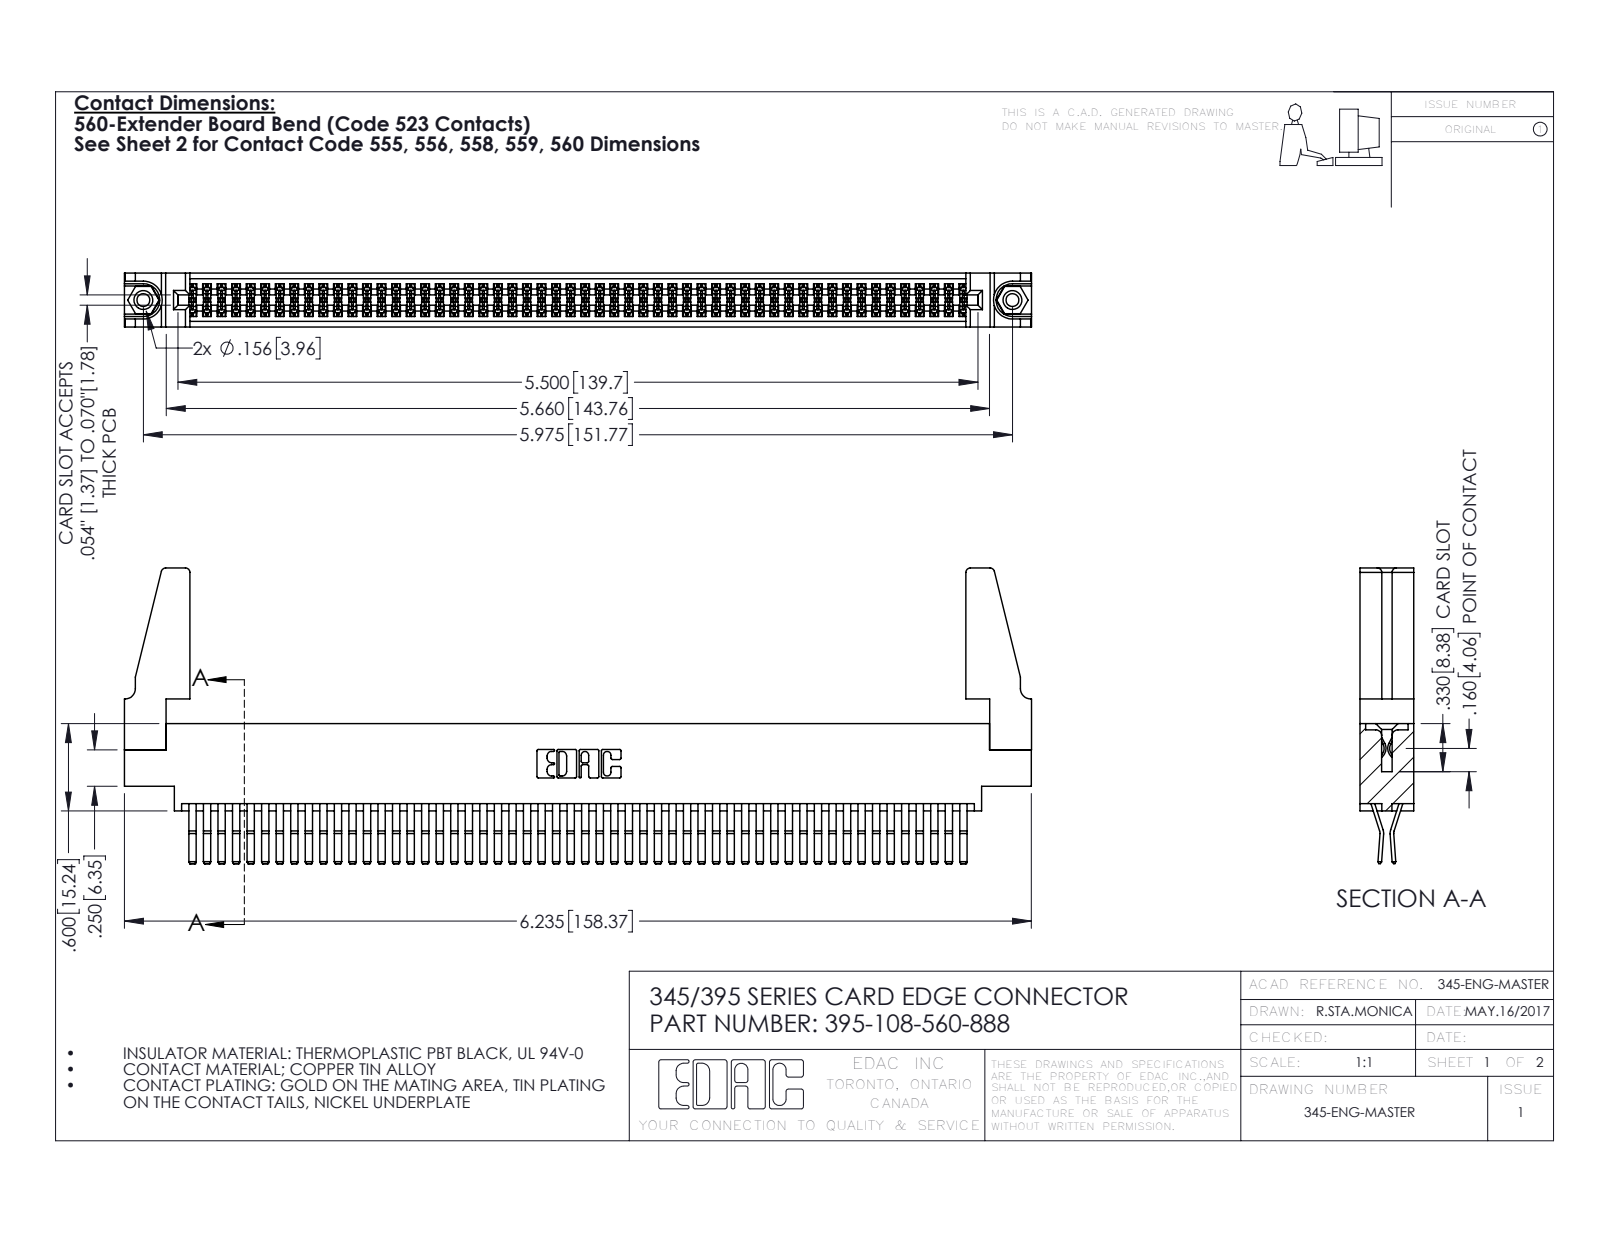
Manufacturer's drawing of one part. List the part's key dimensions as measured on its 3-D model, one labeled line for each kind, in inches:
Part name (STEP PRODUCT): 395-108-560-888; 345-292-001_560 Tail; 345-220-078_345-220-088; 345-250-001_345-250-001-102 (+1 more)
STEP written by: SolidWorks 2016 (CONFIG_CONTROL_DESIGN)
Units: inches
Bodies: 113 solids, 5870 faces (3720 planar, 2134 cylindrical, 16 other)
Overall size (bounding box): 6.236 × 2.032 × 0.37
Volume: 1.181 in³ · Surface area: 45.11 in²
Round holes (diameter × count): ⌀0.089 ×2, ⌀0.125 ×2, ⌀0.156 ×2, ⌀0.064 ×1
Round bosses / shafts (diameter × count): ⌀0.155 ×2
Partial cylindrical surfaces — rounded edges, fillets, slot ends (radius × count): R0.006 ×162, R0.01 ×22, R0.03 ×8, R0.007 ×6, R0.031 ×6, R0.026 ×3, R0.01 ×2, R0.014 ×2
Main face-to-face distances: 0.072, 0.298, 0.025, 0.37, 0.2, 0.098, 0.272, 0.225, 0.175, 0.149
Hole centre spacings: 0.27, 5.739, 5.975
